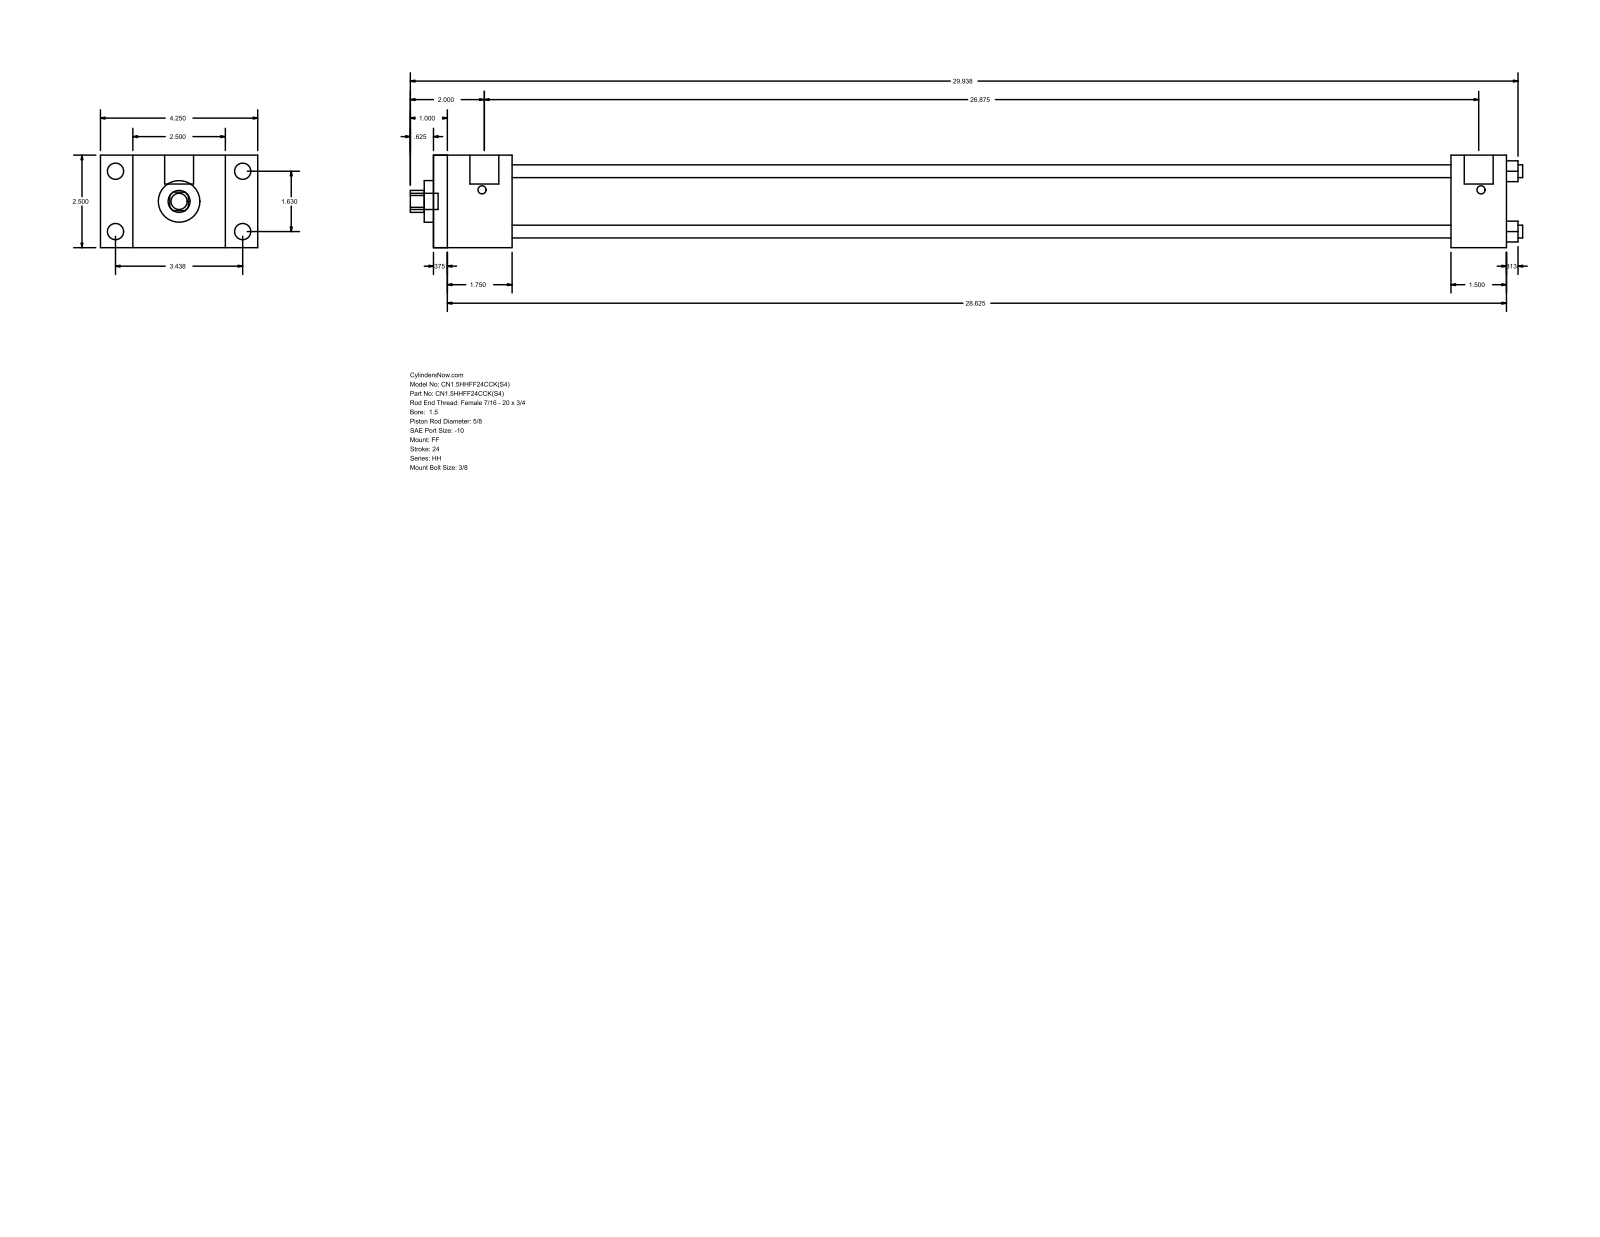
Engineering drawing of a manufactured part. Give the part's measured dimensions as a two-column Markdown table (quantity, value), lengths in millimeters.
| quantity | value |
| --- | --- |
| part name | HH_FF__0150_0.625 |
| STEP written by | GSSL Pune (CONFIG_CONTROL_DESIGN) |
| units | millimeters |
| bodies | 0 solids, 92 faces (64 planar, 28 cylindrical, 0 other) |
| overall size | 763.59 × 107.95 × 63.5 |
| round holes (diameter × count) | 8.76 × 4, 15.88 × 1, 28.57 × 1, 44.45 × 1 |
| round bosses / shafts (diameter × count) | 11.13 × 4, 5.56 × 4, 19.84 × 2, 11.11 × 1 |
| partial cylindrical surfaces (radius × count) | 7.54 × 1 |
| main face-to-face distances | 63.5, 736.6, 9.52, 38.1, 727.08, 53.97, 44.45, 682.63, 698.5, 688.98 |
| hole center spacings | 29.27, 41.4, 58.55 |
